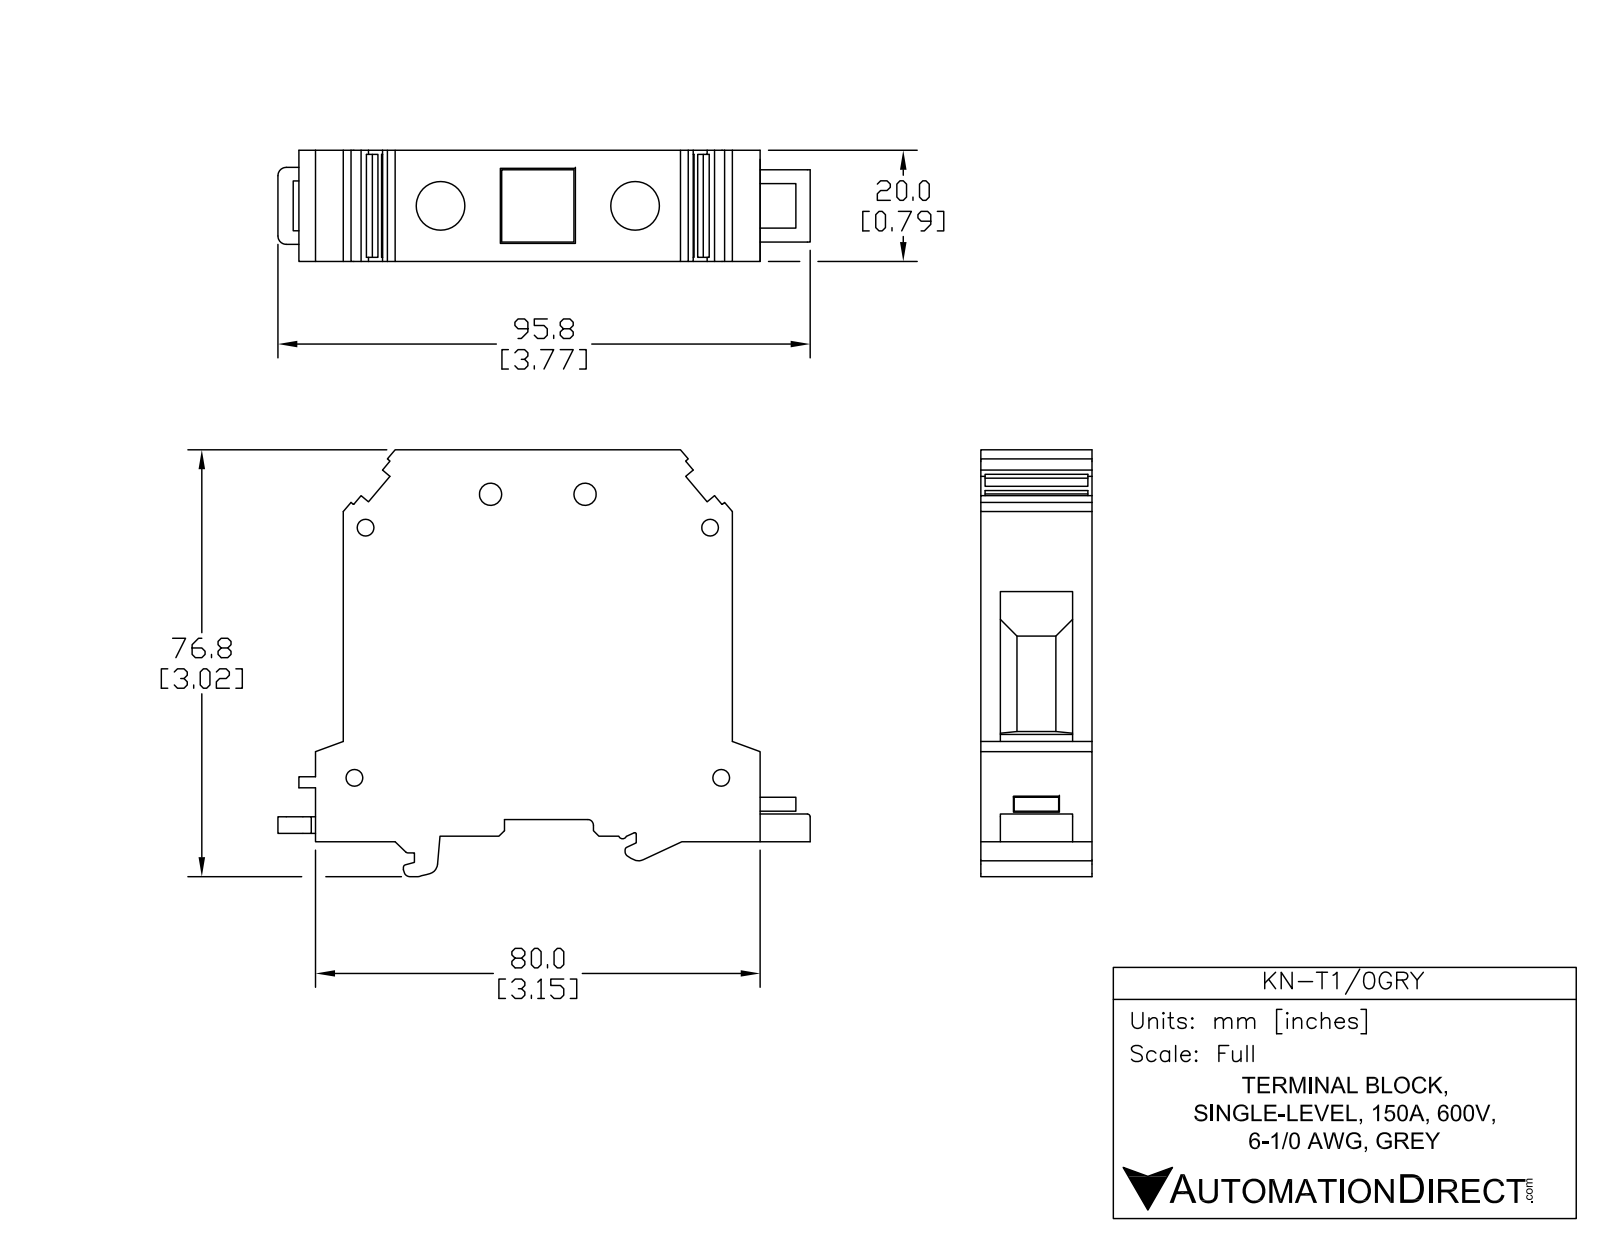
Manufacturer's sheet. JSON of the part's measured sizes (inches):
{"part_name": "KN-T1_0GRY", "step_written_by": "SolidWorks 2019 (CONFIG_CONTROL_DESIGN)", "units": "inches", "bodies": {"solids": 1, "faces": 346, "planar": 257, "cylindrical": 68, "other": 21}, "overall_size": [3.77, 3.027, 0.945], "volume_in3": 5.975, "surface_area_in2": 29.34, "round_holes": [[0.335, 2], [0.079, 1]], "round_bosses_or_shafts": [[0.157, 2]], "partial_cylinders_radius": [[0.039, 9], [0.02, 6], [0.004, 5], [0.012, 5], [0.03, 3], [0.079, 3], [0.049, 2], [0.059, 2]], "face_to_face_distances": [0.787, 0.039, 2.717, 2.776, 0.197, 0.236, 2.913, 2.953, 2.677, 0.138], "hole_center_spacings": [1.378]}
